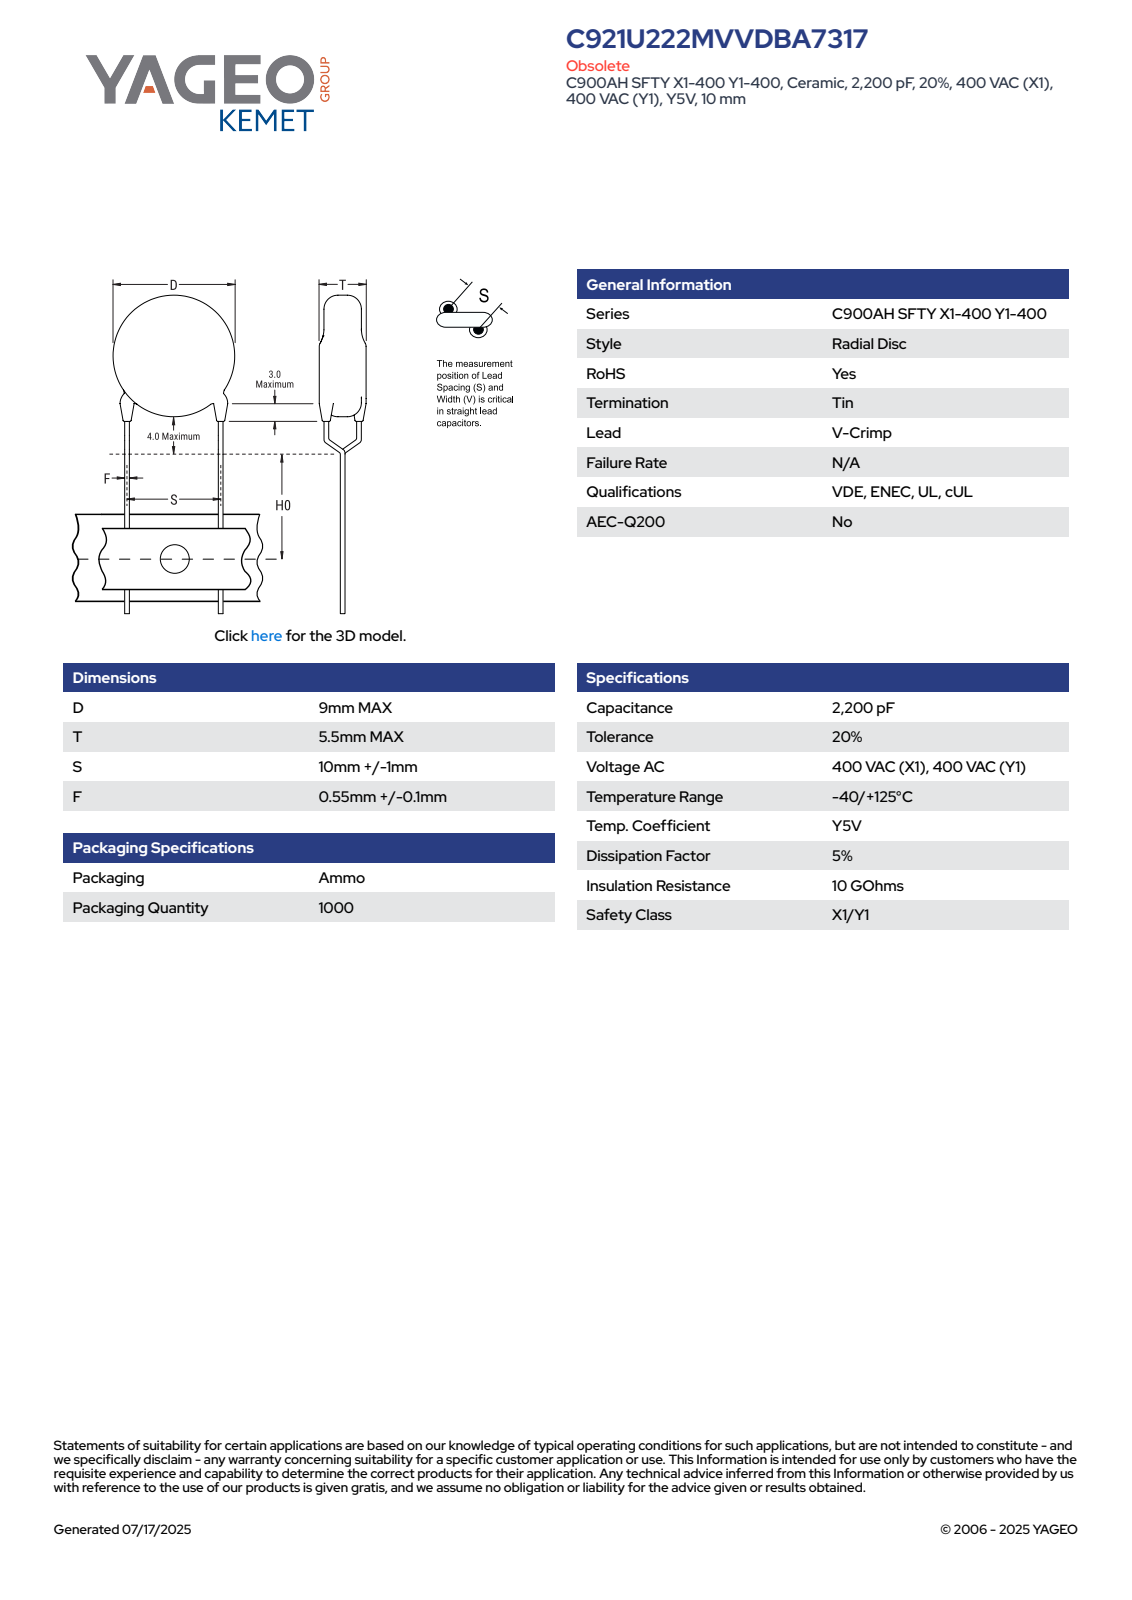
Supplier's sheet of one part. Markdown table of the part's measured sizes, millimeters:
| quantity | value |
| --- | --- |
| part name | CCD_VCC900_D9T5.5S10LL20F0.65 |
| STEP written by | SolidWorks 2014 (AUTOMOTIVE_DESIGN) |
| units | millimeters |
| bodies | 5 solids, 93 faces (65 planar, 16 cylindrical, 12 other) |
| overall size | 32.8 × 10.65 × 5.5 |
| volume | 359 mm³ |
| surface area | 379 mm² |
| round bosses / shafts (diameter × count) | 0.65 × 6, 9 × 1 |
| main face-to-face distances | 5.5, 22.9, 1.17, 28.88, 5.98, 27.71, 4.81, 0.32, 4.77, 3.47 |
